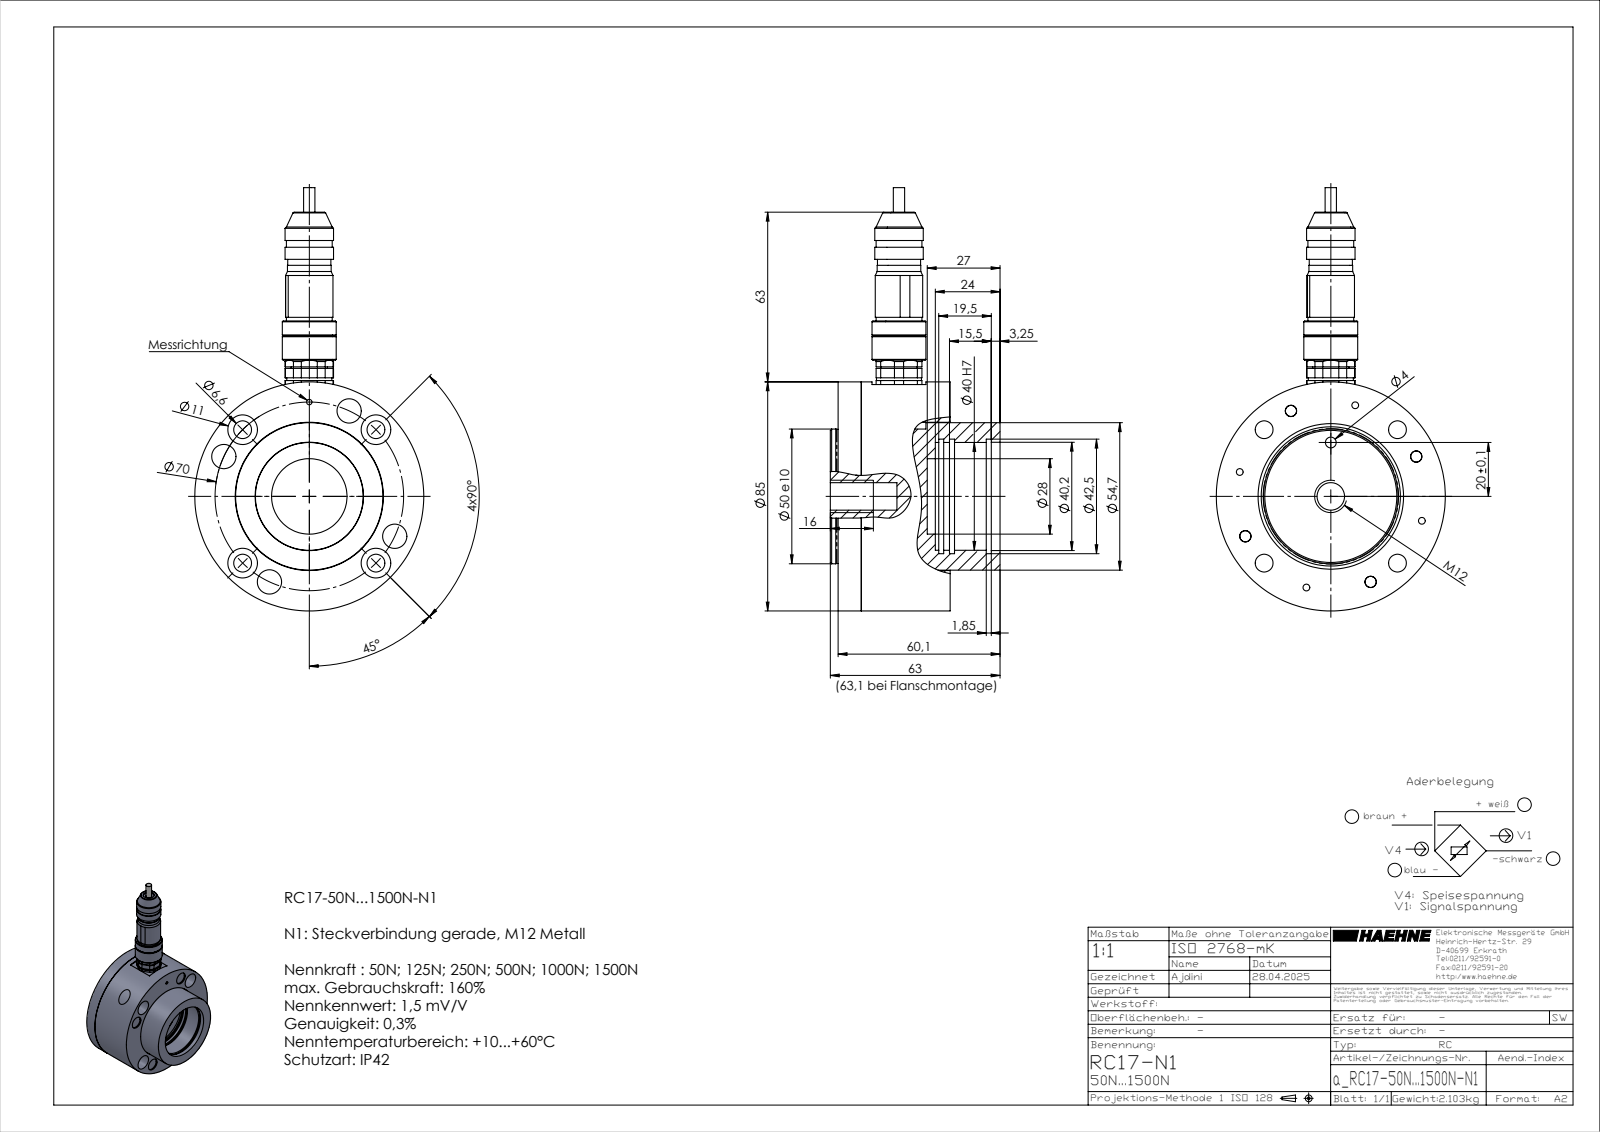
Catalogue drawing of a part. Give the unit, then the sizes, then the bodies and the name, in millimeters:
Units: millimetres
Overall size (bounding box): 157.06 × 85 × 63.1
Round holes (diameter × count): ⌀1 ×5, ⌀2.5 ×4, ⌀3.4 ×4, ⌀4.2 ×4, ⌀5.3 ×4, ⌀6.6 ×4, ⌀9 ×4, ⌀11 ×4, ⌀2 ×1, ⌀4 ×1, ⌀4.5 ×1, ⌀8.2 ×1
Round bosses / shafts (diameter × count): ⌀8.5 ×4, ⌀5.7 ×4, ⌀5 ×4, ⌀3 ×4, ⌀1.5 ×4, ⌀1 ×4, ⌀85 ×1, ⌀54.7 ×1
Partial cylindrical surfaces — rounded edges, fillets, slot ends (radius × count): R0.3 ×6, R1 ×4, R0.57 ×1, R0.6 ×1, R0.77 ×1, R3.5 ×1
Main face-to-face distances: 8.6, 3, 11.6, 33, 44.6, 41.6, 11.5, 2.9, 44.5, 2
Hole centre spacings: 35, 34.99, 49.49, 49.5, 70, 23.94, 40.15, 67.61
Volume: 258 461 mm³ · Surface area: 79 214 mm²
Bodies: 15 solids, 475 faces (236 planar, 155 cylindrical, 84 other)
Part name (STEP PRODUCT): a_RC-N2 Flanschmontage Scheibe; a_RC17-50N...1500N-N1; a_RC17-50N...1500N-N1 STEPP
STEP written by: SolidWorks 2023 (AUTOMOTIVE_DESIGN)
